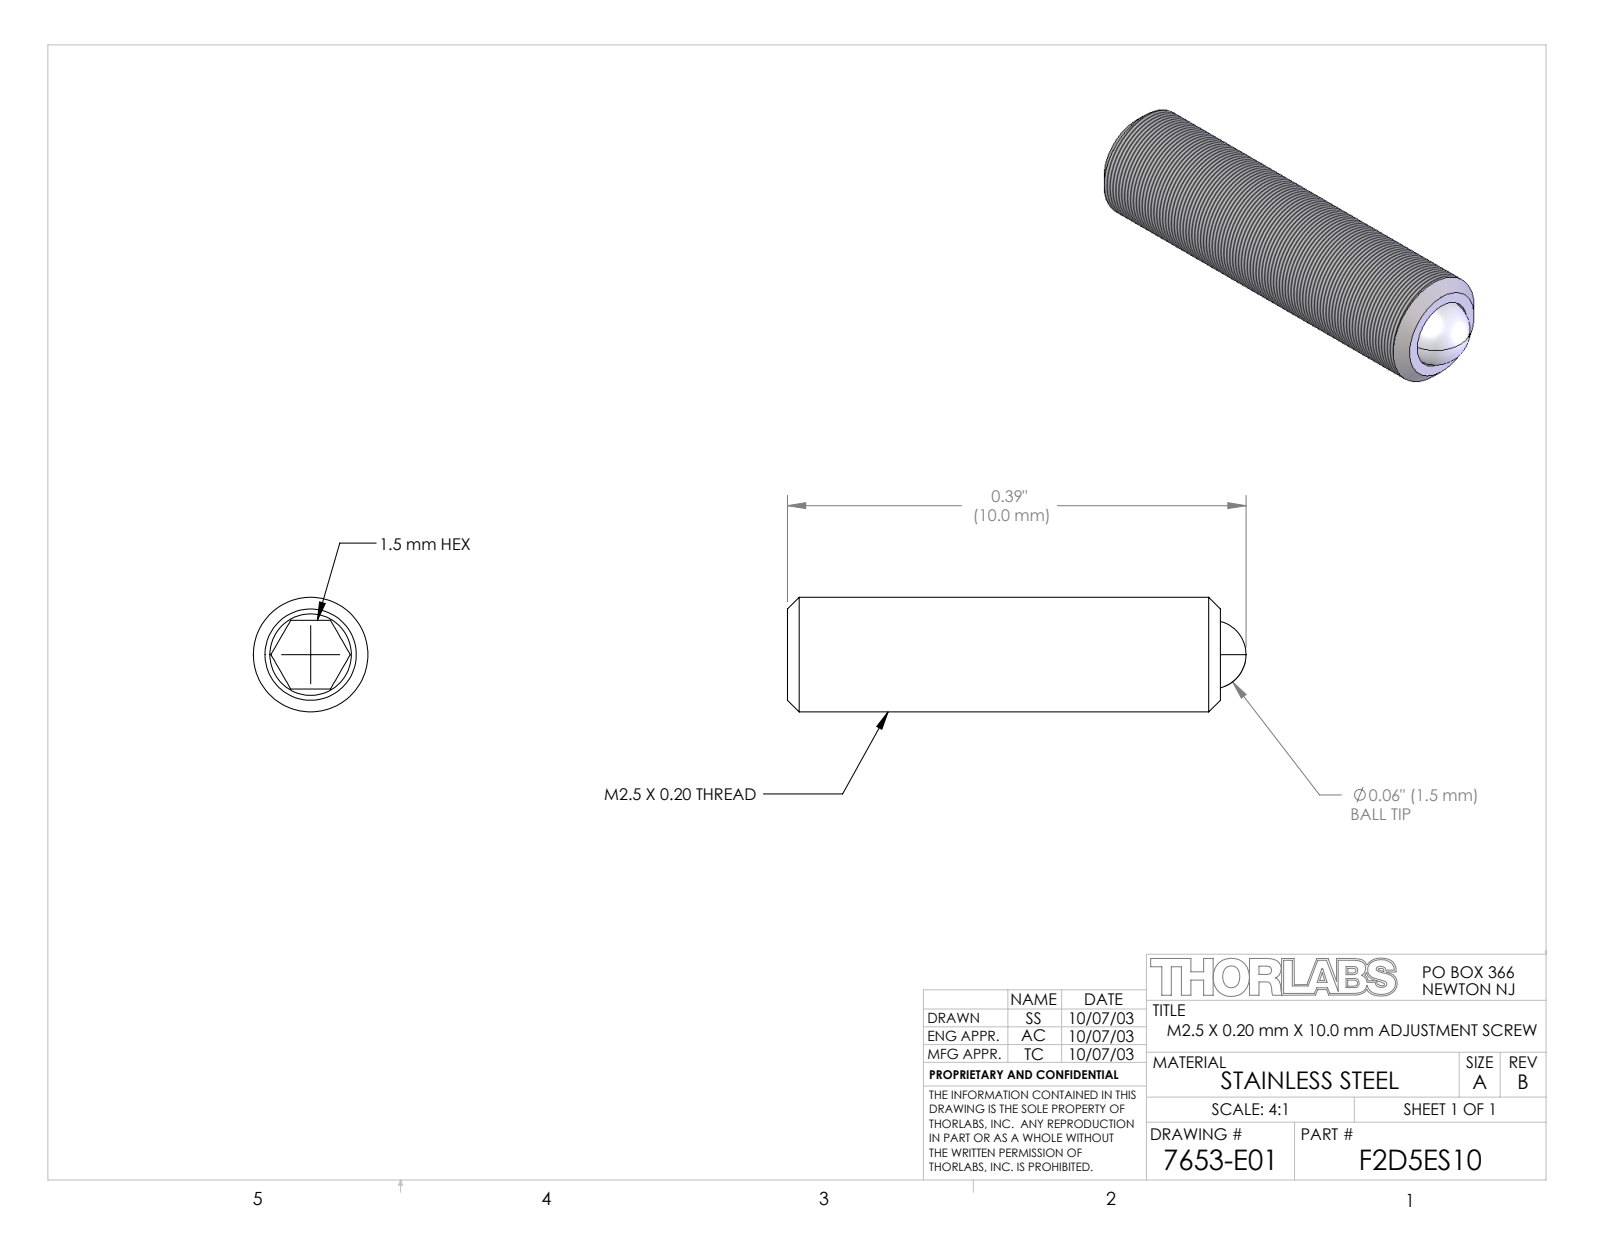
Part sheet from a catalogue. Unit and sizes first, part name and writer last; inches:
Units: inches
Overall size (bounding box): 0.394 × 0.098 × 0.098
Round holes (diameter × count): ⌀0.059 ×1
Round bosses / shafts (diameter × count): ⌀0.098 ×1
Main face-to-face distances: 0.059, 0.252, 0.372, 0.12
Volume: 0.002 in³ · Surface area: 0.166 in²
Bodies: 2 solids, 25 faces (9 planar, 4 cylindrical, 12 other)
Part name (STEP PRODUCT): 7653-E0W
STEP written by: SolidWorks 2011 (AUTOMOTIVE_DESIGN)
